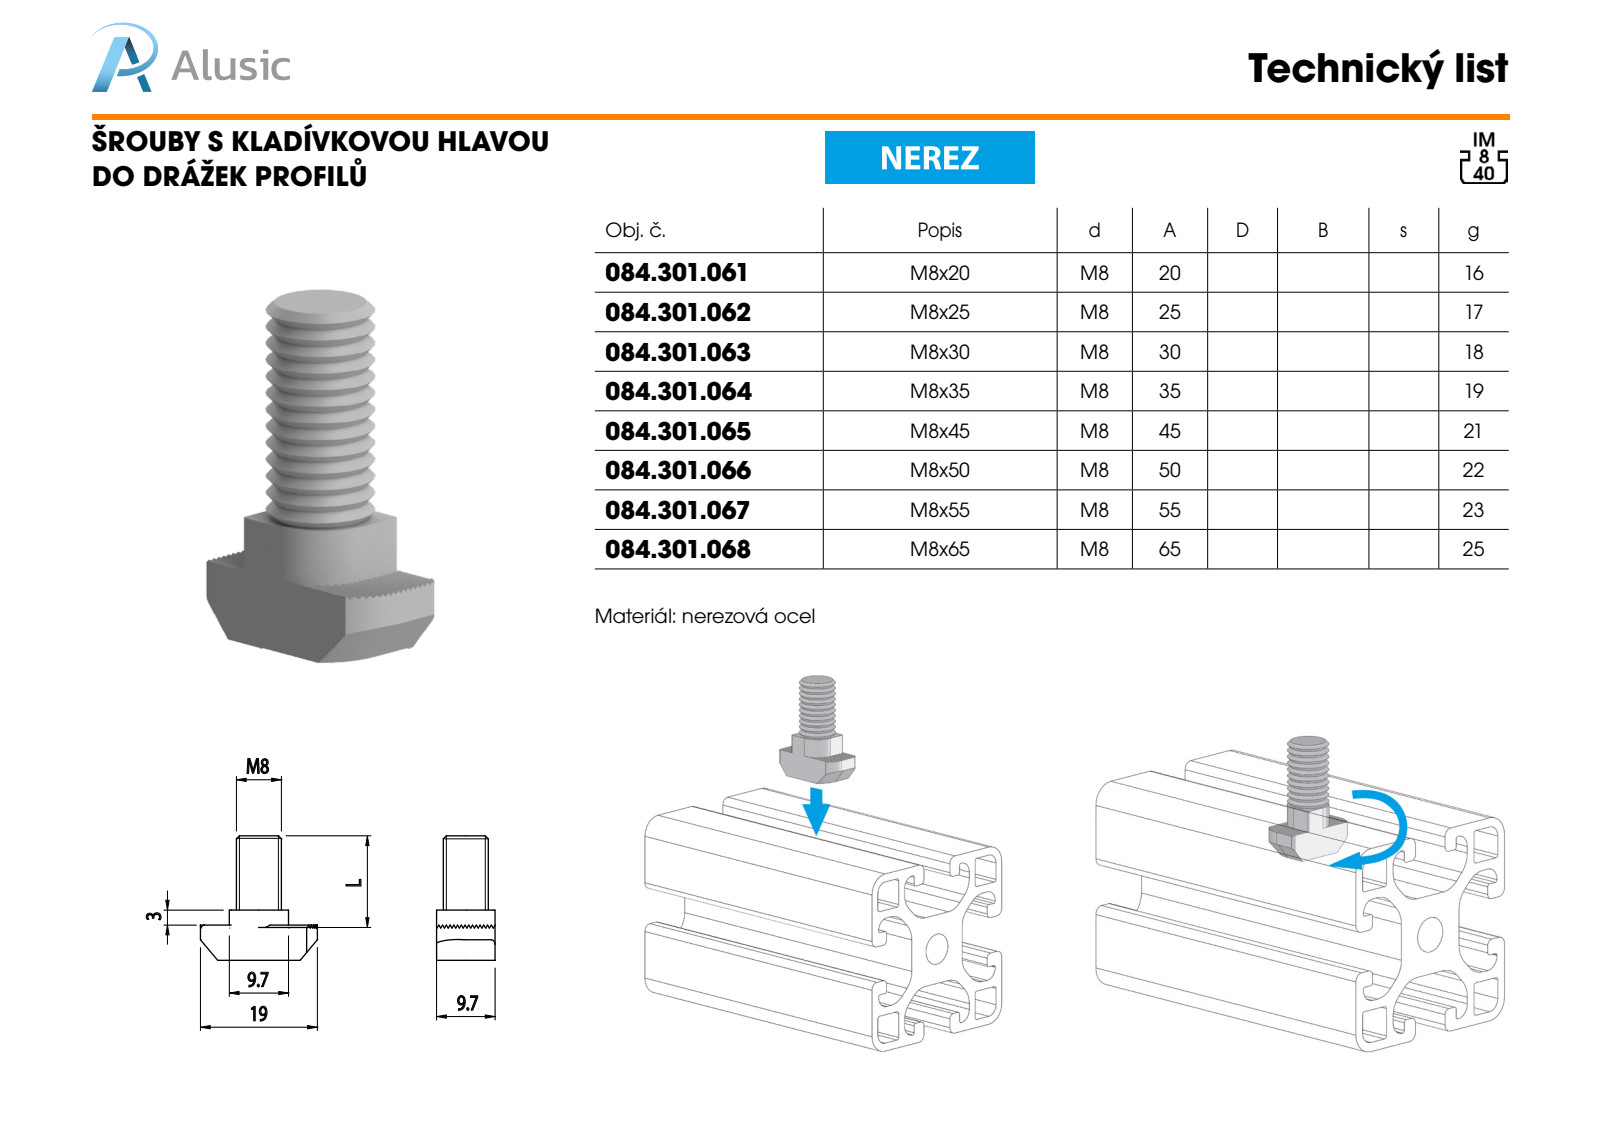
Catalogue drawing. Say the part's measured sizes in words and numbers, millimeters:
The part is named "084.301.063". Its 3-D file was written by "SolidWorks 2016 (CONFIG_CONTROL_DESIGN)". It is 1 solid with 139 faces: 92 planar, 44 cylindrical and 3 other. Overall it measures 35 by 19 by 9.7 millimeters. Its volume is 2 297 cubic millimeters and its surface area 1 650 square millimeters. Round bosses or shafts: 1 of diameter 8. Partial cylindrical surfaces (rounded edges, fillets, slot ends): 2 of radius 0.3, 2 of radius 5, 1 of radius 4.85. The main face-to-face distances are 0.35, 0.7, 1.05, 9.7, 1.4, 1.75, 2.1, 2.45, 2.8, 3.15.
